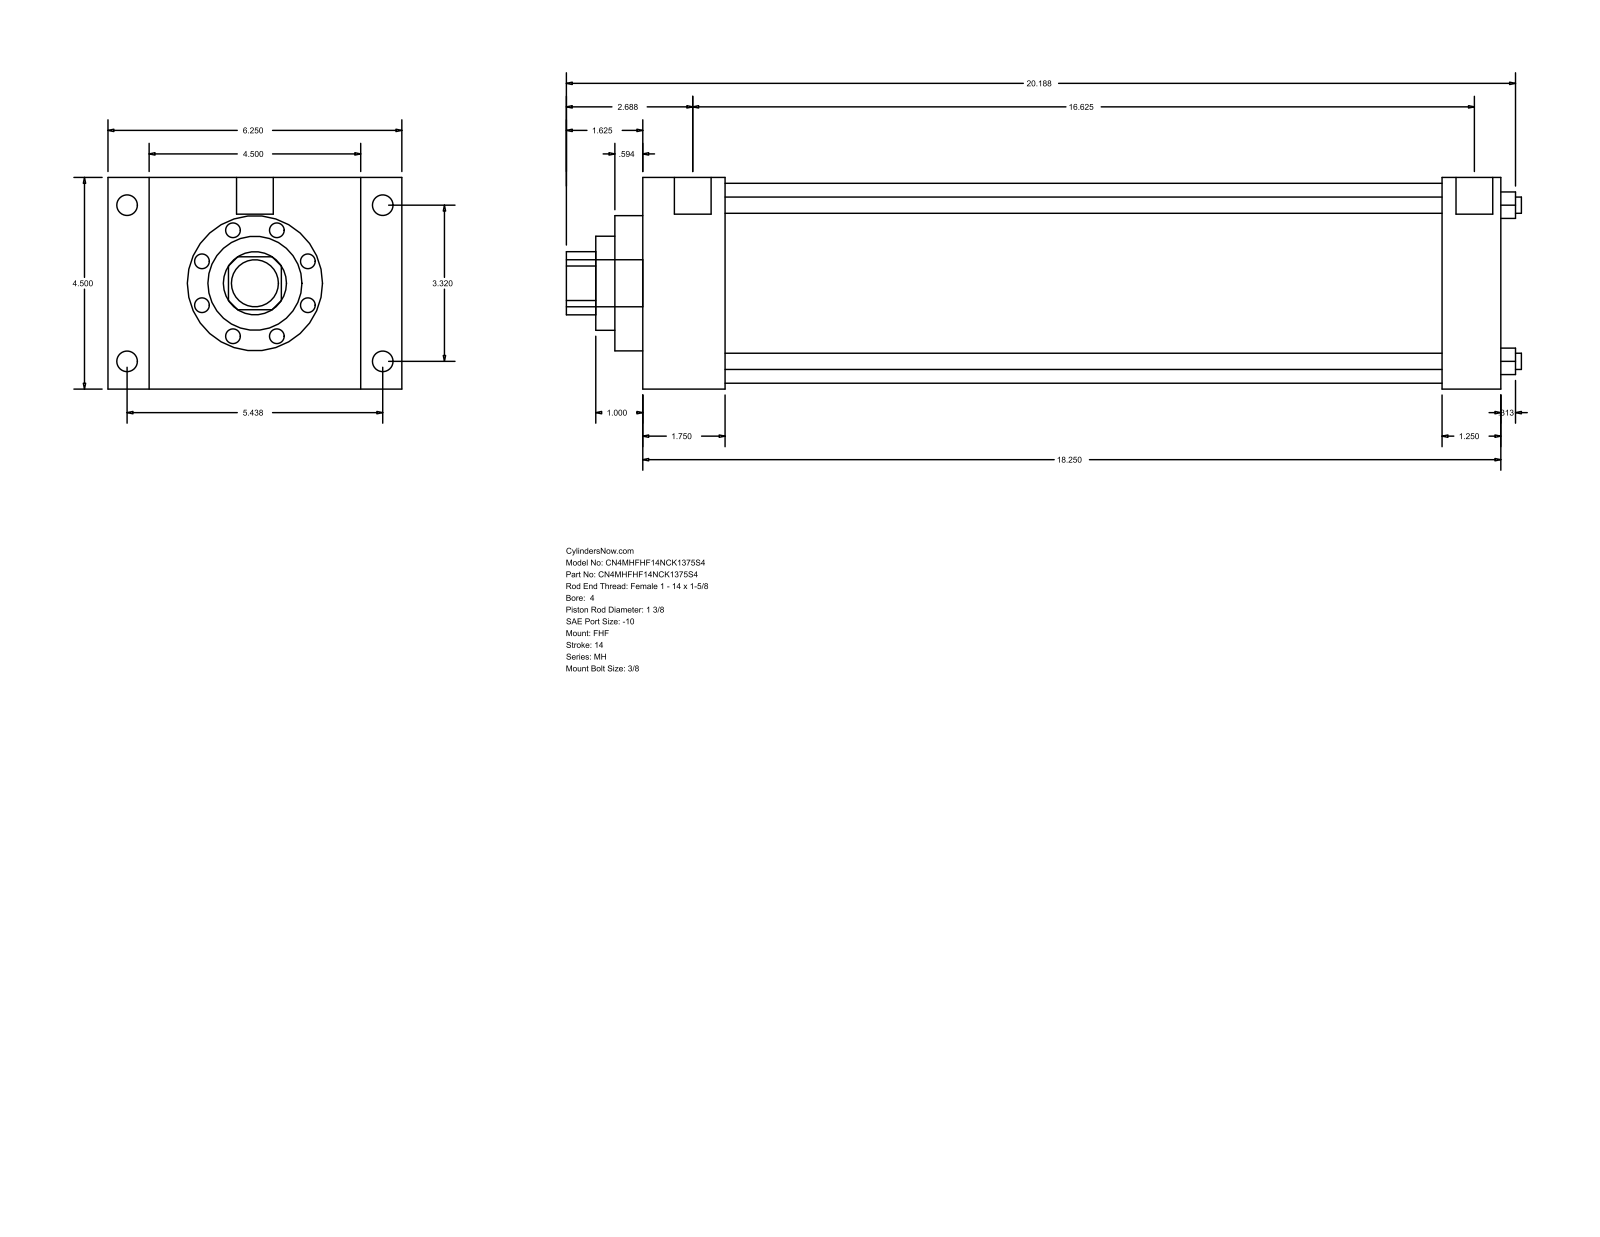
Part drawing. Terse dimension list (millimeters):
name: MH_FHF__0400_1.375
written by: GSSL Pune (CONFIG_CONTROL_DESIGN)
unit: mm
bodies: 0 solids, 90 faces (61 planar, 29 cylindrical, 0 other)
size: 515.94 × 158.75 × 114.3
holes: 4× ⌀8.76, 1× ⌀34.92, 1× ⌀50.8, 1× ⌀73.03, 1× ⌀107.95
bosses: 4× ⌀11.13, 4× ⌀8.73, 2× ⌀19.84, 1× ⌀25.4
rounds: 1× R17.06
face distances: 114.3, 463.55, 44.45, 419.1, 22.23, 136.53, 158.76, 431.8, 387.35, 31.75
hole spacings: 59.62, 84.32, 119.25
